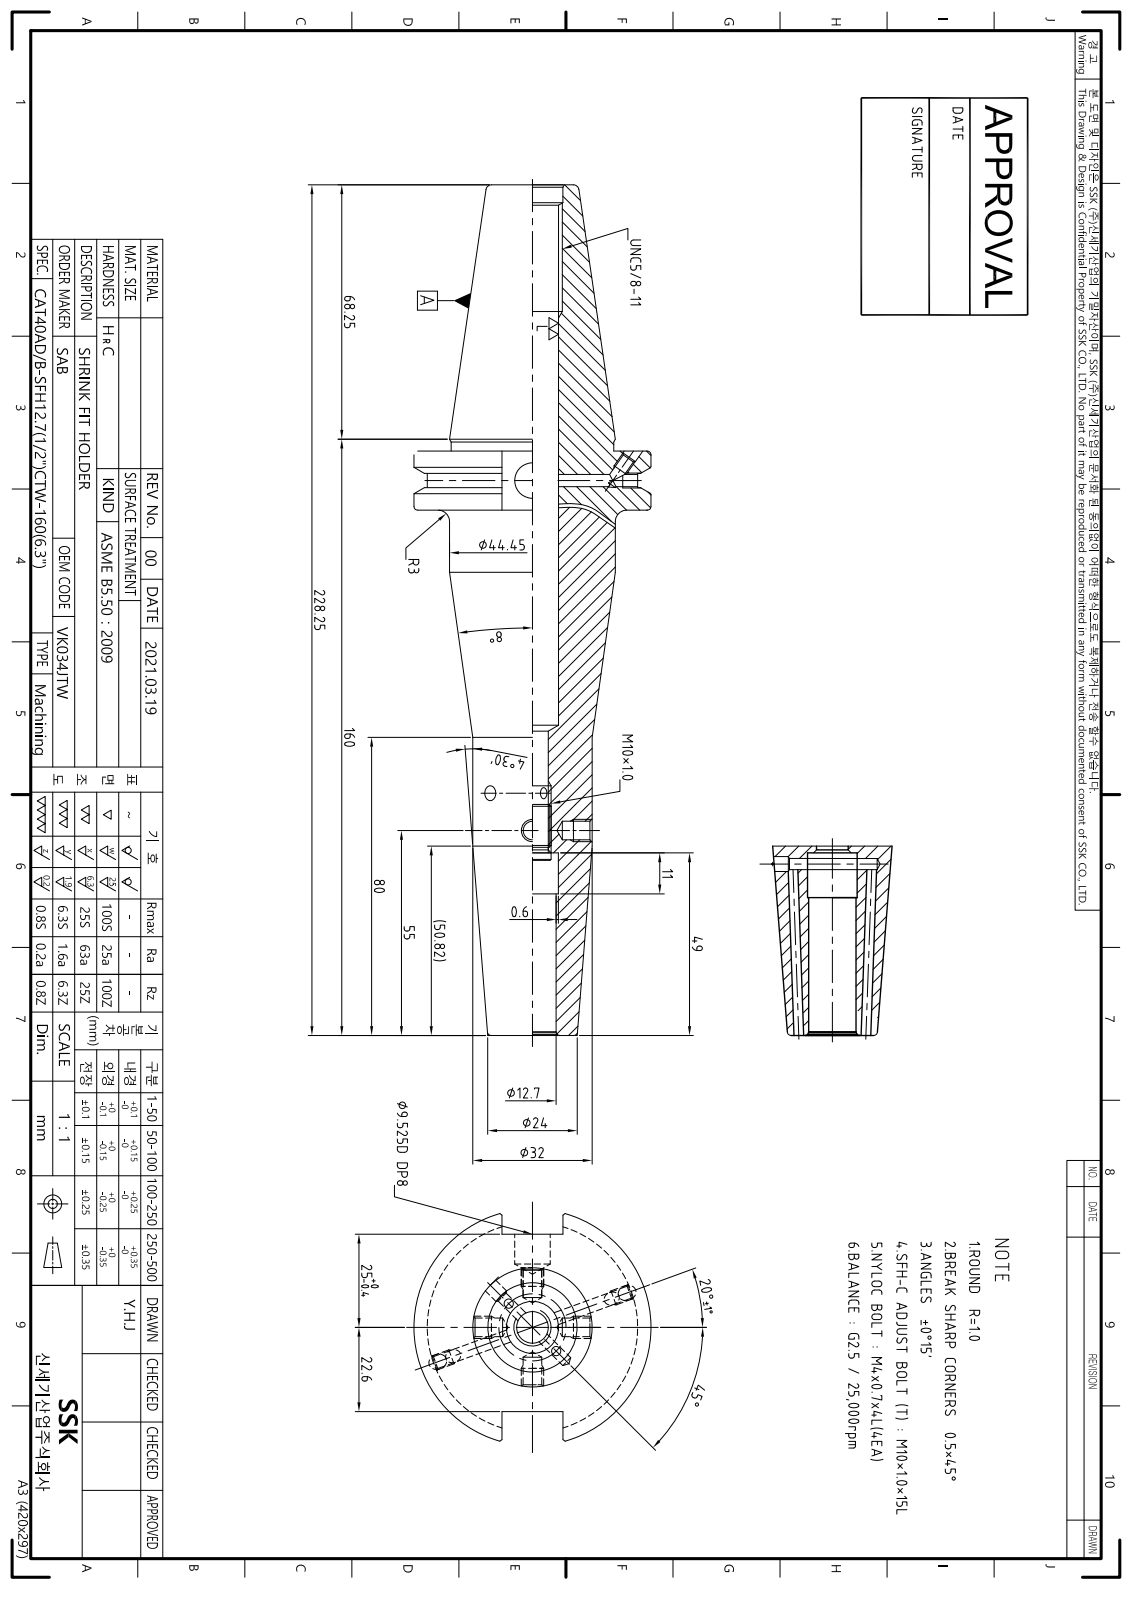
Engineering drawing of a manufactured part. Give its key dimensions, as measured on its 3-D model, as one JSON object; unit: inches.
{"part_name": "LO-CAT40ADB-SFH12.7CTW-160", "step_written_by": "Autodesk Inventor 2024 (AUTOMOTIVE_DESIGN)", "units": "inches", "bodies": {"solids": 1, "faces": 91, "planar": 37, "cylindrical": 32, "other": 22}, "overall_size": [8.986, 2.5, 2.405], "volume_in3": 13.2, "surface_area_in2": 62.98, "round_holes": [[0.128, 4], [0.079, 2], [0.157, 2], [0.165, 2], [0.351, 1], [0.375, 1], [0.5, 1], [0.512, 1], [0.527, 1], [0.547, 1], [0.642, 1]], "round_bosses_or_shafts": [[2.5, 1], [1.75, 1], [1.717, 1], [1.26, 1]], "partial_cylinders_radius": [[1.108, 1]], "face_to_face_distances": [0.625, 6.174, 5.549, 1.874, 0.645, 2.812, 3.437, 8.986, 3.05, 0.238]}
